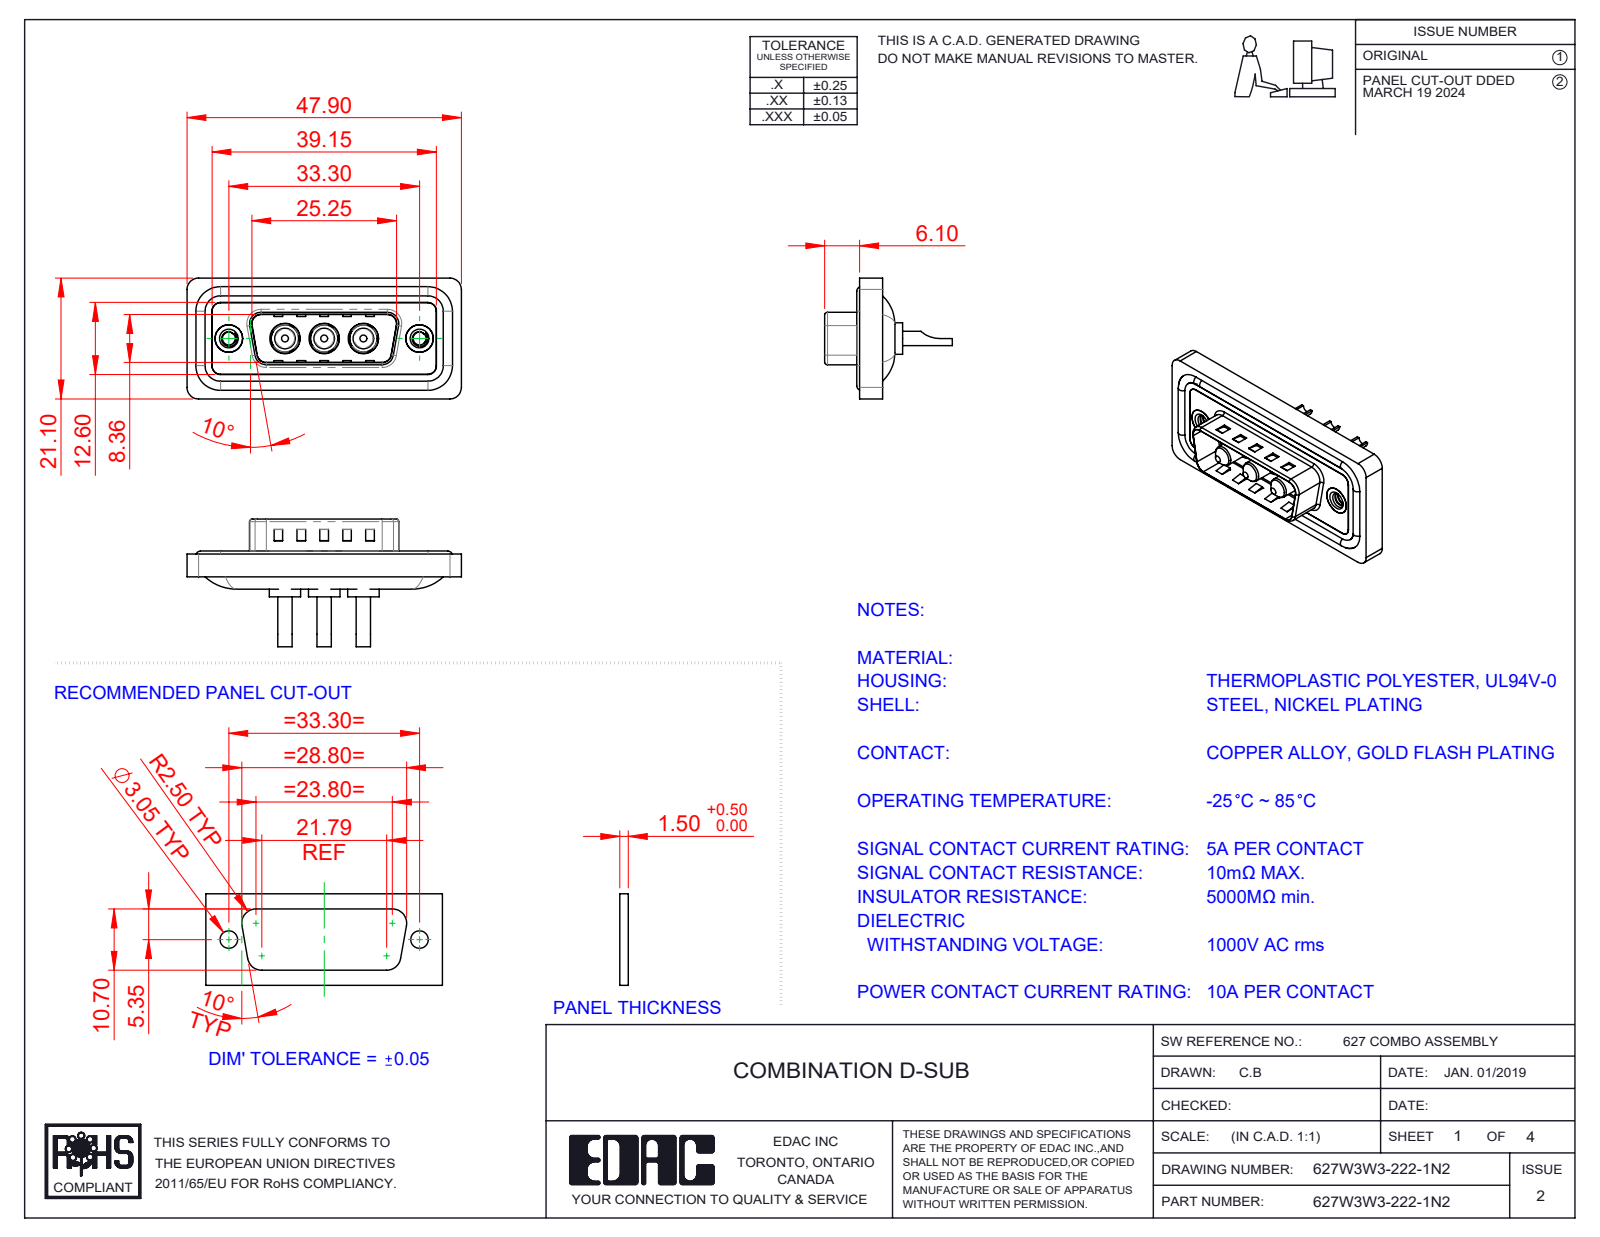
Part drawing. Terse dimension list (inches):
name: 627W3W3-222-1N2; 627Combo Threaded Rivet_2; Power Pin_10A SC; 627Combo Shell Front_15 Contacts (+3 more)
written by: SolidWorks 2023 (CONFIG_CONTROL_DESIGN)
unit: in
bodies: 13 solids, 582 faces (213 planar, 250 cylindrical, 119 other)
size: 1.886 × 0.878 × 0.831
volume: 0.34 in³; area: 13.79 in²
holes: 3× ⌀0.067, 3× ⌀0.191, 3× ⌀0.209, 2× ⌀0.089, 2× ⌀0.157, 2× ⌀0.189, 2× ⌀0.197
bosses: 4× ⌀0.063, 3× ⌀0.217, 3× ⌀0.205, 3× ⌀0.187, 3× ⌀0.148, 3× ⌀0.142, 3× ⌀0.098, 2× ⌀0.193
rounds: 26× R0.059, 20× R0.079, 8× R0.02, 8× R0.063, 4× R0.01, 4× R0.024, 4× R0.026, 4× R0.035
face distances: 0.016, 0.043, 0.059, 0.02, 0.063, 0.122, 0.114, 0.157, 0.032, 0.377
hole spacings: 0.27, 0.386, 0.656, 0.925, 0.539, 1.311
